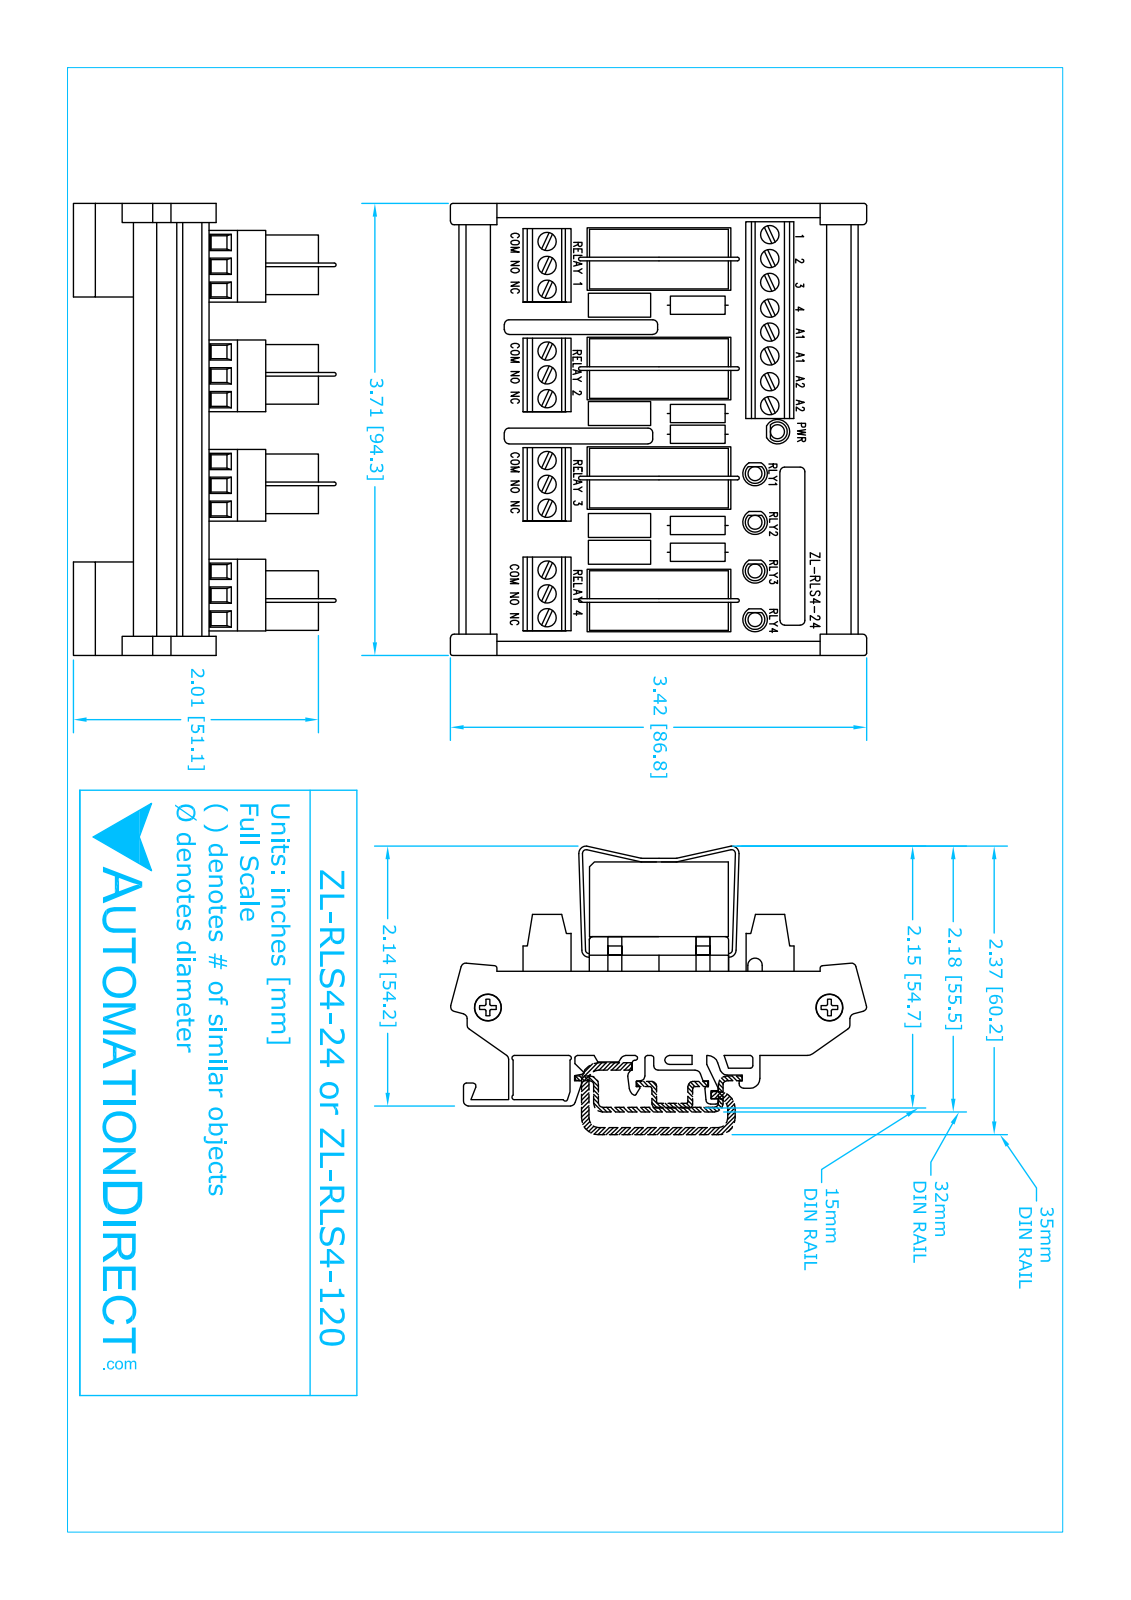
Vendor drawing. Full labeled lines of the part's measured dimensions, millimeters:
Part name (STEP PRODUCT): ZL-RLS4-120
STEP written by: SolidWorks 2014 (AUTOMOTIVE_DESIGN)
Units: millimetres
Bodies: 2 solids, 1066 faces (686 planar, 225 cylindrical, 155 other)
Overall size (bounding box): 95.7 × 86.9 × 55.5
Volume: 104 600 mm³ · Surface area: 65 550 mm²
Round holes (diameter × count): ⌀3.8 ×20, ⌀5.7 ×2
Round bosses / shafts (diameter × count): ⌀3.8 ×5, ⌀5.2 ×2
Partial cylindrical surfaces — rounded edges, fillets, slot ends (radius × count): R0.4 ×58, R0.8 ×24
Main face-to-face distances: 11, 3.5, 14.5, 16, 12.5, 1.4, 23.1, 2, 92.2, 7.3
Hole centre spacings: 22.9, 5.1, 45.7, 10.2, 15.2, 4.9, 4.9, 9.8
